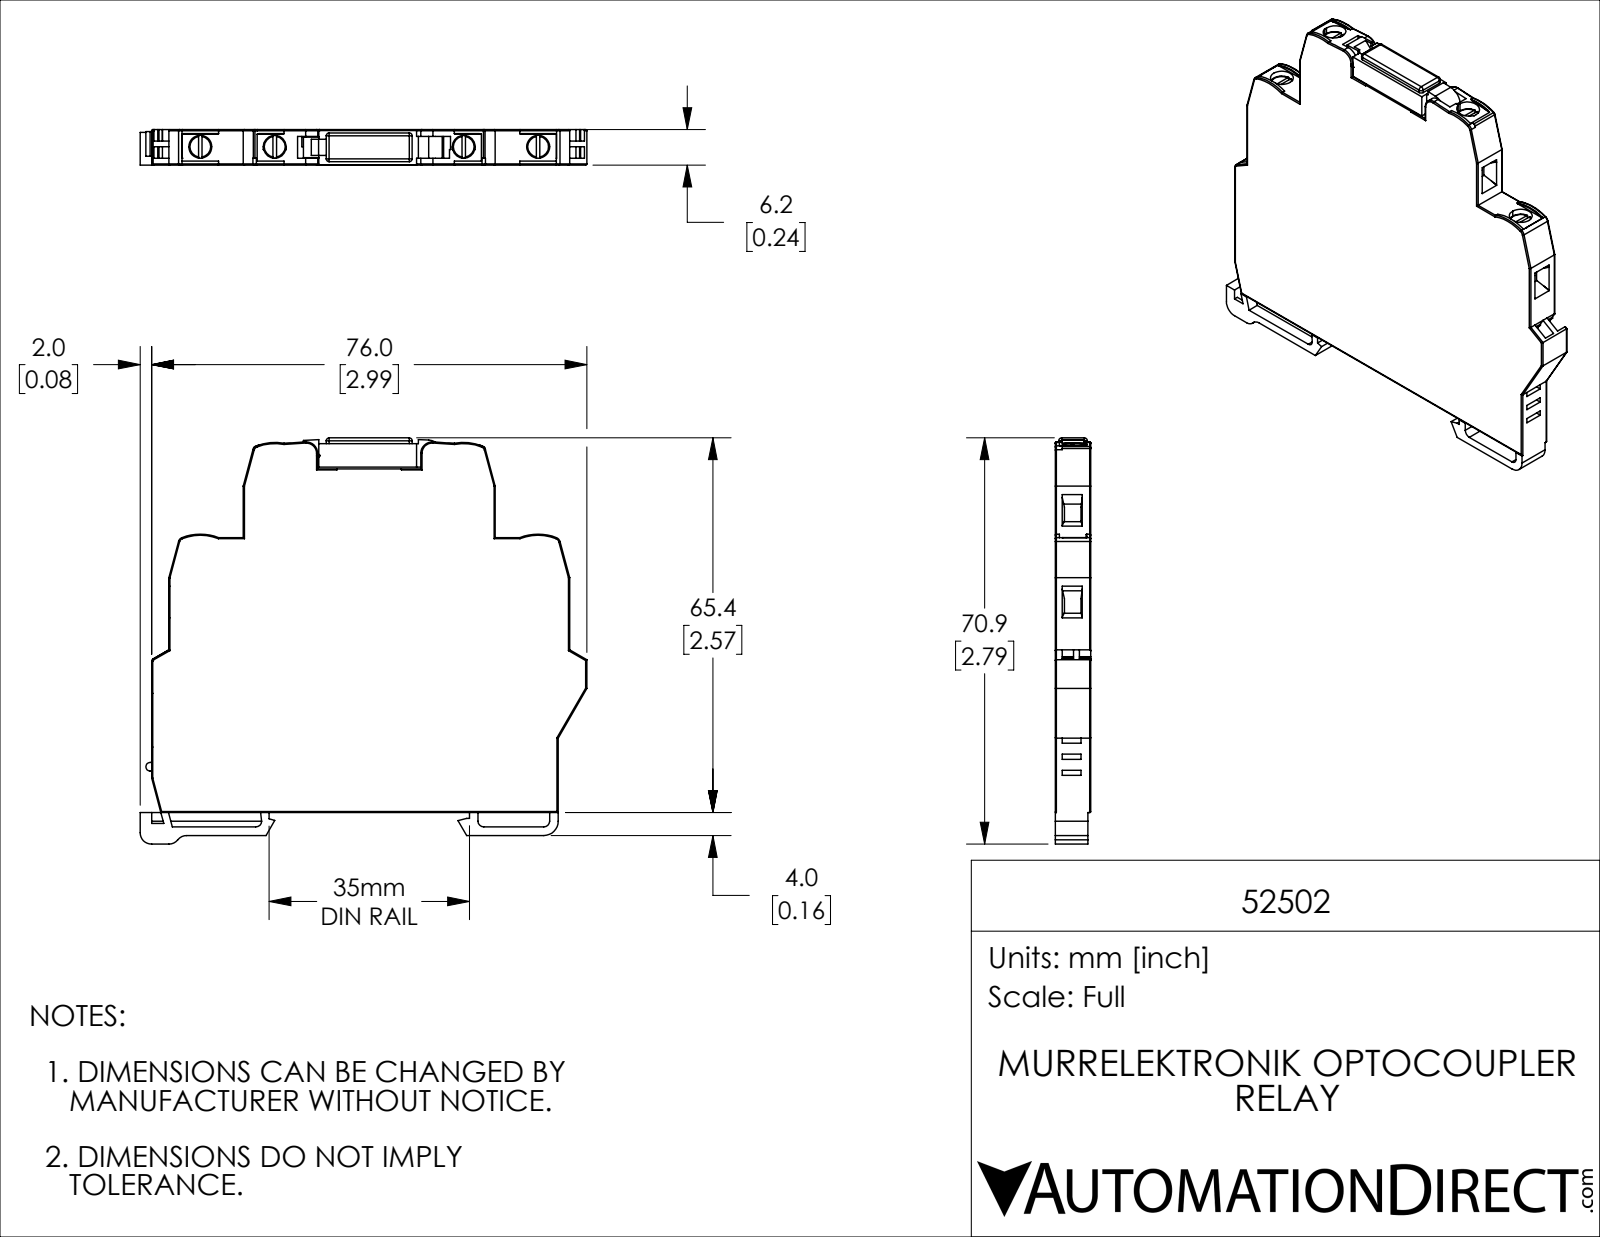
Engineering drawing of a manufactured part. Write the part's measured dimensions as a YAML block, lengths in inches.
part_name: "52502"
step_written_by: "SolidWorks 2019 (CONFIG_CONTROL_DESIGN)"
units: inches
bodies: {solids: 2, faces: 496, planar: 298, cylindrical: 138, other: 60}
overall_size: [3.071, 2.791, 0.244]
volume: 1.561
surface_area: 18.26
round_holes:
  - {diameter: 0.157, count: 4}
  - {diameter: 0.075, count: 1}
round_bosses_or_shafts:
  - {diameter: 0.079, count: 1}
partial_cylinders:
  - {radius: 0.008, count: 50}
  - {radius: 0.02, count: 11}
  - {radius: 0.039, count: 7}
  - {radius: 0.079, count: 6}
  - {radius: 0.03, count: 5}
  - {radius: 0.005, count: 4}
  - {radius: 0.346, count: 4}
  - {radius: 0.016, count: 3}
face_to_face_distances: [0.244, 0.059, 0.197, 0.118, 0.098, 2.362, 0.157, 0.079, 0.047, 0.02]
hole_center_spacings: [0.512, 1.811, 1.299, 2.323]
